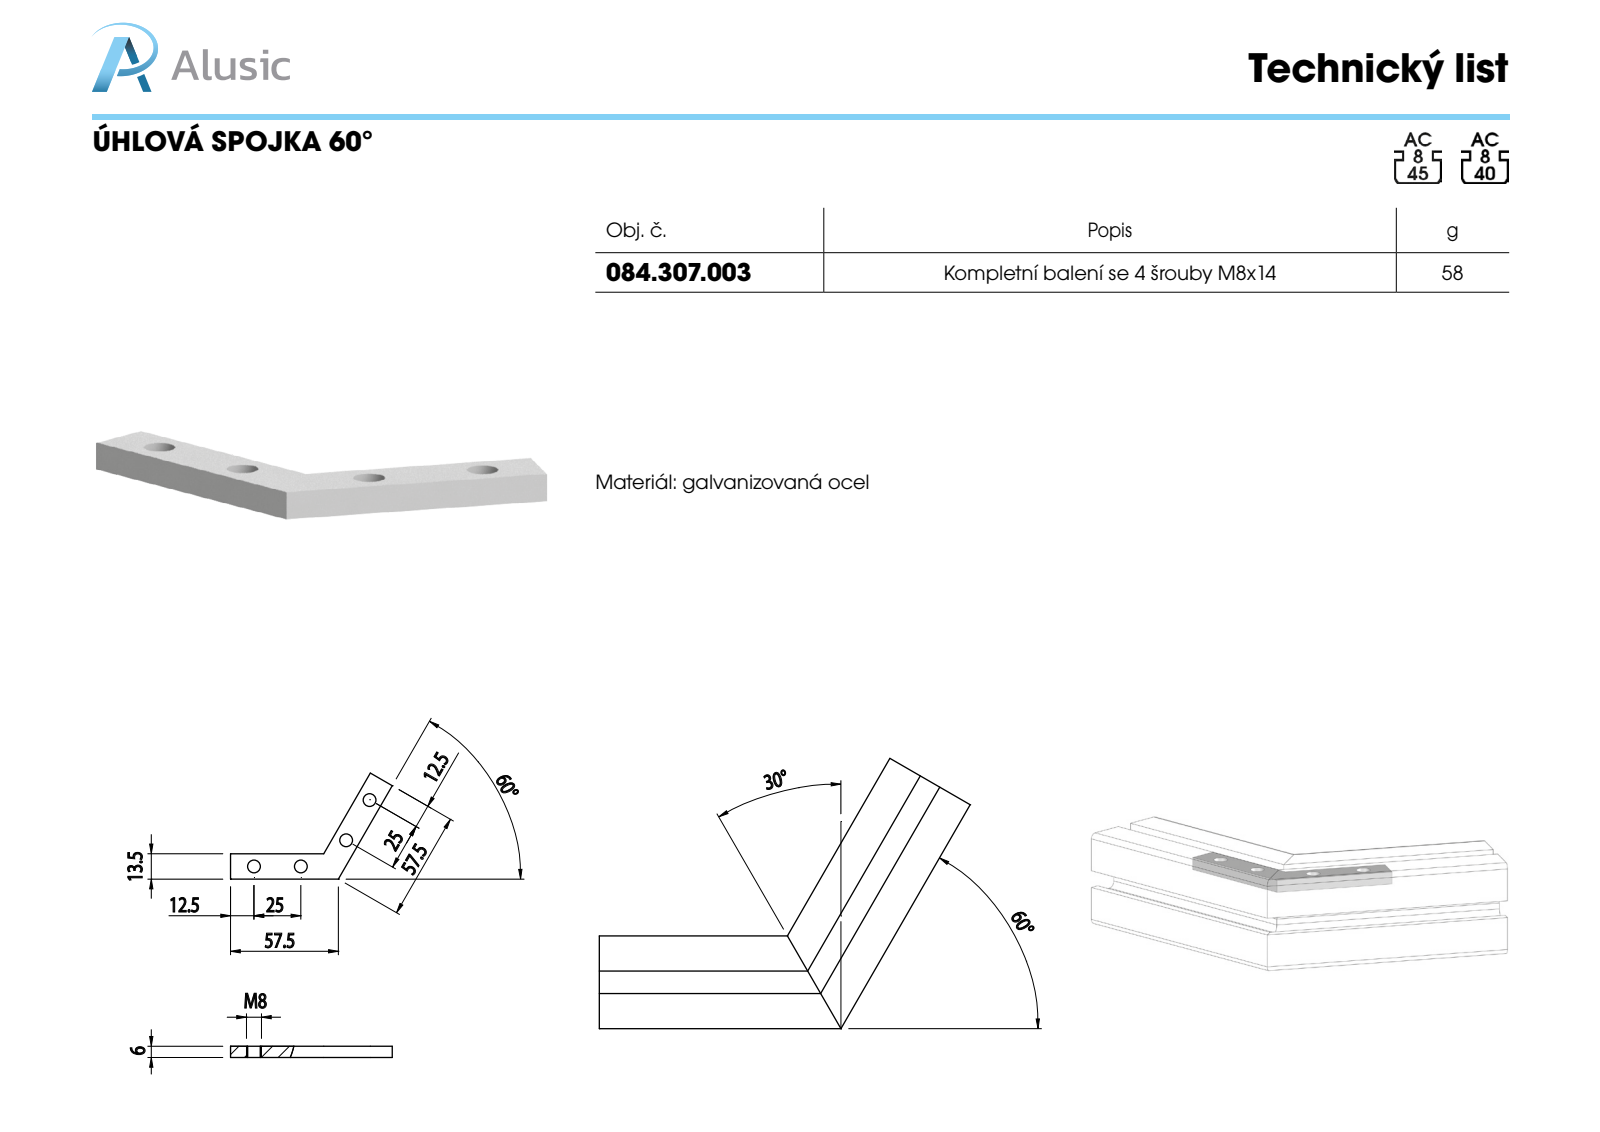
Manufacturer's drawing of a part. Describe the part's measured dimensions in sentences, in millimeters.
The part is named "084.307.003". Its 3-D file was written by "SolidWorks 2011 (CONFIG_CONTROL_DESIGN)". It is 1 solid with 16 faces: 8 planar, 8 cylindrical and 0 other. Overall it measures 86.25 by 56.55 by 6 millimeters. Its volume is 7 812 cubic millimeters and its surface area 4 565 square millimeters. Round holes: 4 of diameter 6.8. The main face-to-face distances are 6, 13.5. The hole center spacings are 25, 51.09, 27.89, 71.19.
